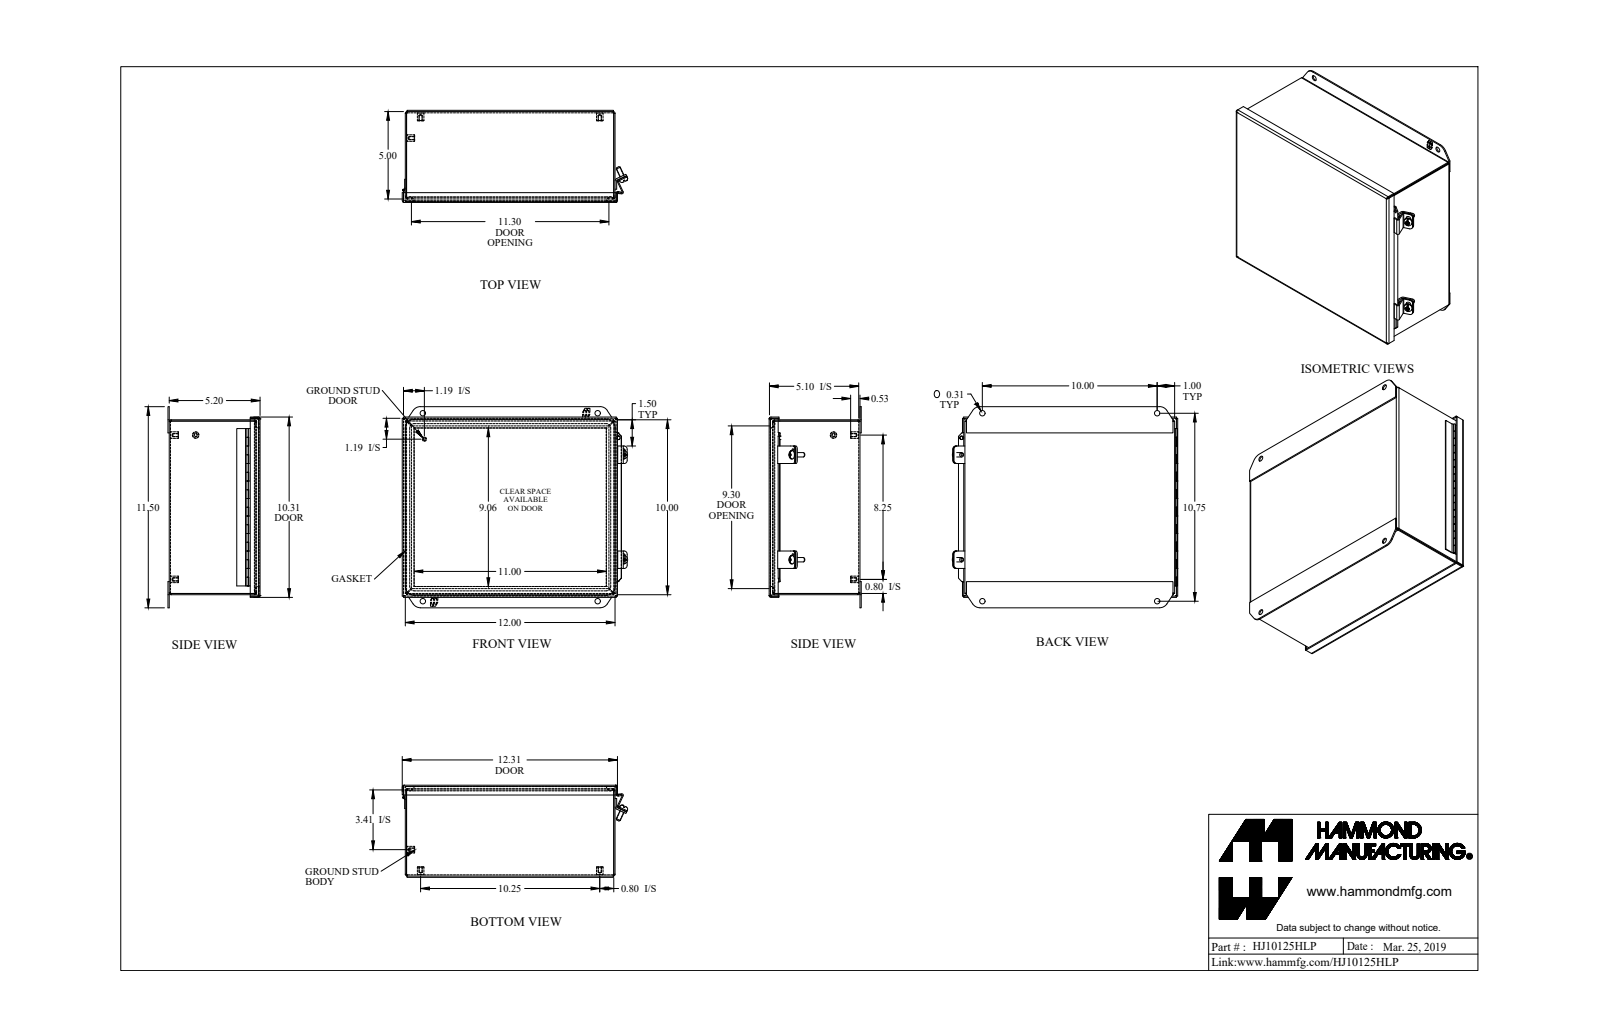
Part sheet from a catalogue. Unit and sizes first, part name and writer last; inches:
Units: inches
Overall size (bounding box): 12.896 × 11.5 × 5.269
Round holes (diameter × count): ⌀0.156 ×5, ⌀0.313 ×4, ⌀0.213 ×2, ⌀0.05 ×1
Round bosses / shafts (diameter × count): ⌀0.375 ×5, ⌀0.25 ×3, ⌀0.48 ×2, ⌀0.188 ×1, ⌀0.1 ×1, ⌀0.045 ×1
Partial cylindrical surfaces — rounded edges, fillets, slot ends (radius × count): R0.25 ×16, R0.036 ×13, R0.108 ×13, R0.188 ×8, R0.01 ×4, R0.141 ×4, R0.499 ×4, R0.5 ×4
Main face-to-face distances: 0.072, 5.125, 5.197, 5.053, 9.928, 11.928, 10, 9.856, 12, 11.856
Hole centre spacings: 10.202, 1.256, 1.257, 8.25, 9.5, 9.501, 10, 10.25
Volume: 43.17 in³ · Surface area: 1 210 in²
Bodies: 20 solids, 740 faces (398 planar, 215 cylindrical, 127 other)
Part name (STEP PRODUCT): HJ10125HLP
STEP written by: SolidWorks 2018 (AUTOMOTIVE_DESIGN)
